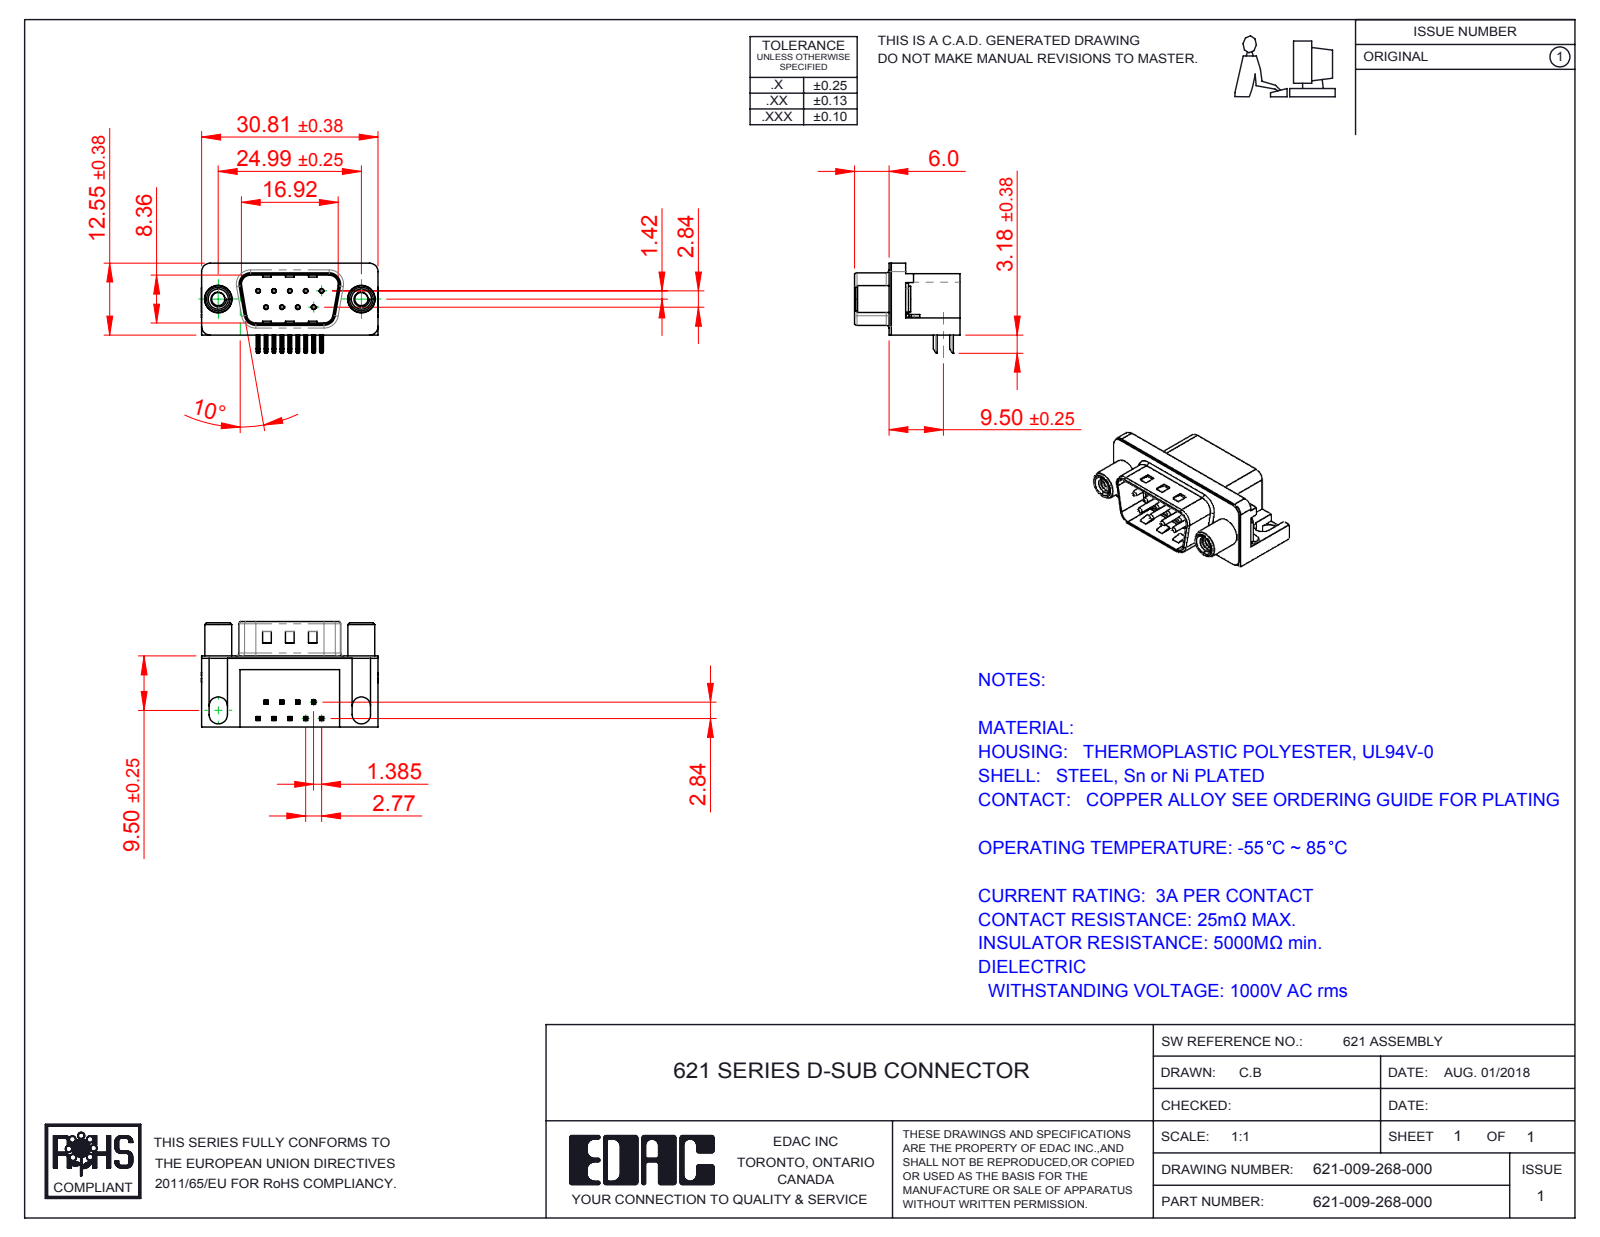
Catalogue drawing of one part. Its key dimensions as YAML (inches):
part_name: "621 Contact Top; 621 Housing_9 Socket; 621 Round Threaded Standoff; 621-009-268-000 (+3 more)"
step_written_by: "SolidWorks 2016 (CONFIG_CONTROL_DESIGN)"
units: inches
bodies: {solids: 15, faces: 979, planar: 563, cylindrical: 319, other: 97}
overall_size: [1.216, 0.724, 0.619]
volume: 0.201
surface_area: 6.893
round_holes:
  - {diameter: 0.014, count: 9}
  - {diameter: 0.031, count: 9}
  - {diameter: 0.091, count: 2}
  - {diameter: 0.122, count: 2}
  - {diameter: 0.157, count: 2}
  - {diameter: 0.189, count: 2}
  - {diameter: 0.197, count: 2}
round_bosses_or_shafts:
  - {diameter: 0.03, count: 9}
  - {diameter: 0.193, count: 2}
  - {diameter: 0.185, count: 2}
  - {diameter: 0.177, count: 2}
  - {diameter: 0.152, count: 2}
partial_cylinders:
  - {radius: 0.01, count: 36}
  - {radius: 0.005, count: 18}
  - {radius: 0.039, count: 16}
  - {radius: 0.02, count: 9}
  - {radius: 0.059, count: 8}
  - {radius: 0.063, count: 8}
  - {radius: 0.035, count: 4}
  - {radius: 0.079, count: 4}
face_to_face_distances: [0.016, 0.472, 0.488, 0.407, 0.114, 0.374, 0.098, 0.083, 0.014, 0.421]
hole_center_spacings: [0.124, 0.109, 0.218, 0.198, 0.198, 0.327, 0.294, 0.295]
